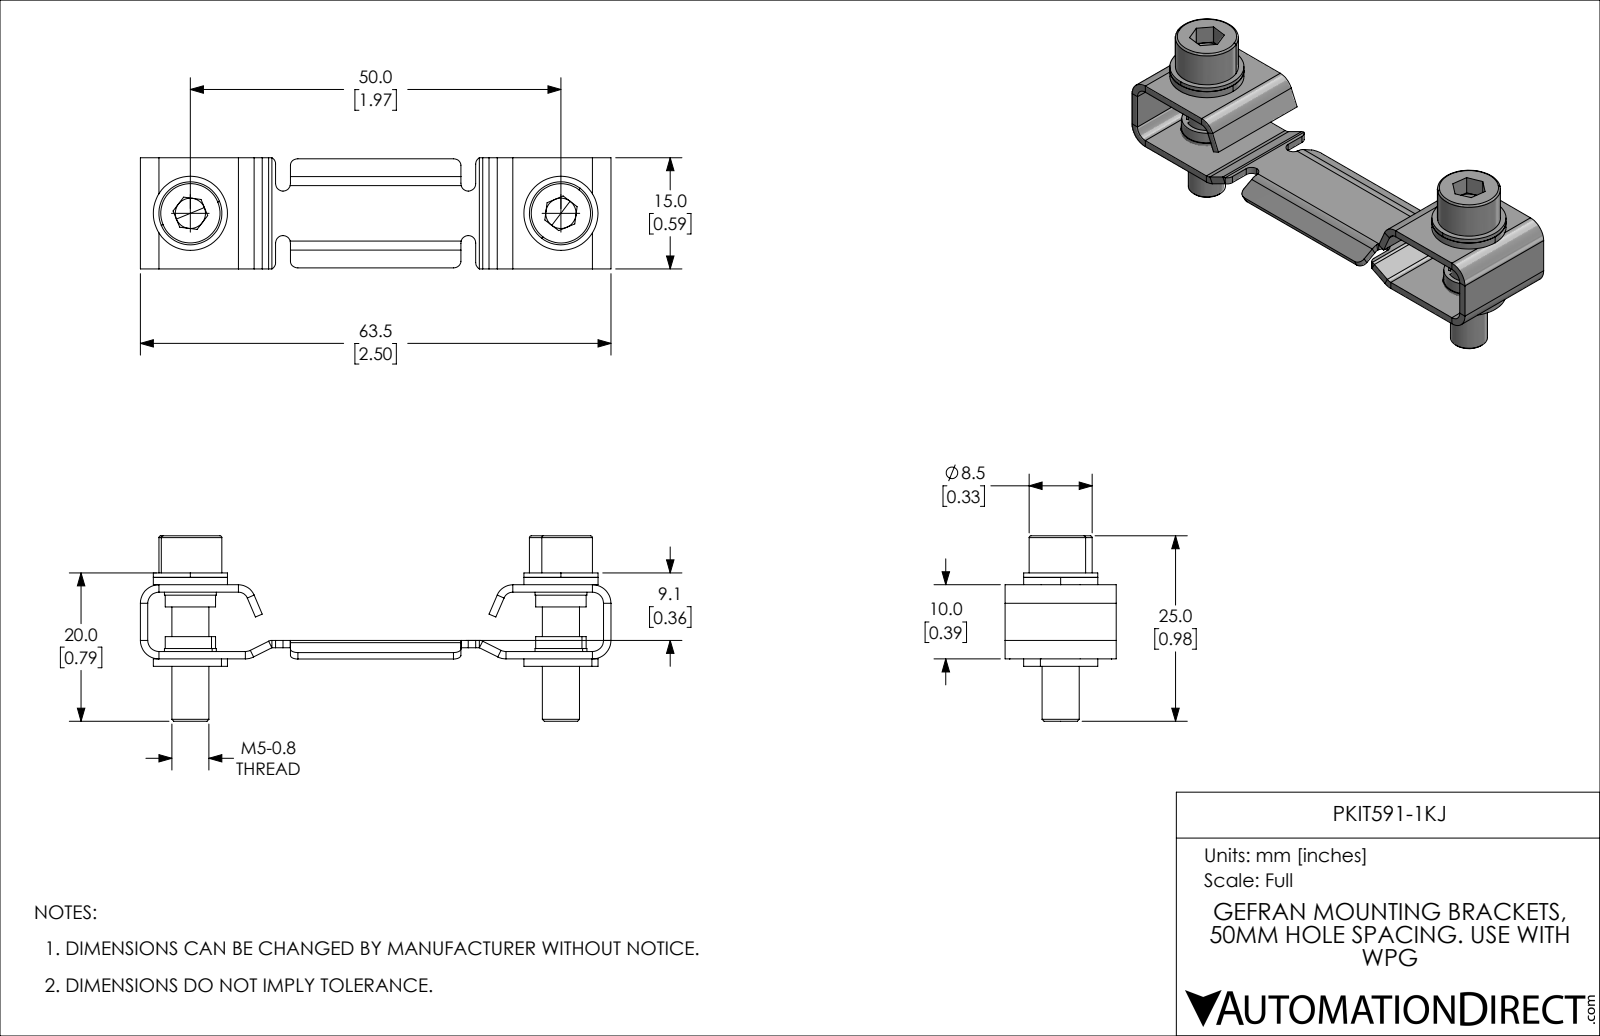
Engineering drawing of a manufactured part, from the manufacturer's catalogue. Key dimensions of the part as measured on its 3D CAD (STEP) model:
Part name (STEP PRODUCT): PKIT591-1KJ
STEP written by: SolidWorks 2021 (CONFIG_CONTROL_DESIGN)
Units: millimetres
Bodies: 9 solids, 336 faces (176 planar, 144 cylindrical, 16 other)
Overall size (bounding box): 63.5 × 25 × 15
Volume: 3 267 mm³ · Surface area: 6 032 mm²
Round holes (diameter × count): ⌀5.5 ×2, ⌀5.9 ×2
Round bosses / shafts (diameter × count): ⌀10 ×2, ⌀8.5 ×2, ⌀7 ×2, ⌀6.8 ×2, ⌀5 ×2
Partial cylindrical surfaces — rounded edges, fillets, slot ends (radius × count): R0.45 ×16, R1 ×14, R0.5 ×12, R1.5 ×8, R2.5 ×8, R1.3 ×2, R2.3 ×2, R2.65 ×2
Main face-to-face distances: 1, 10, 9, 1.5, 7.5, 8.5, 2, 2.5, 8, 11
Hole centre spacings: 50
